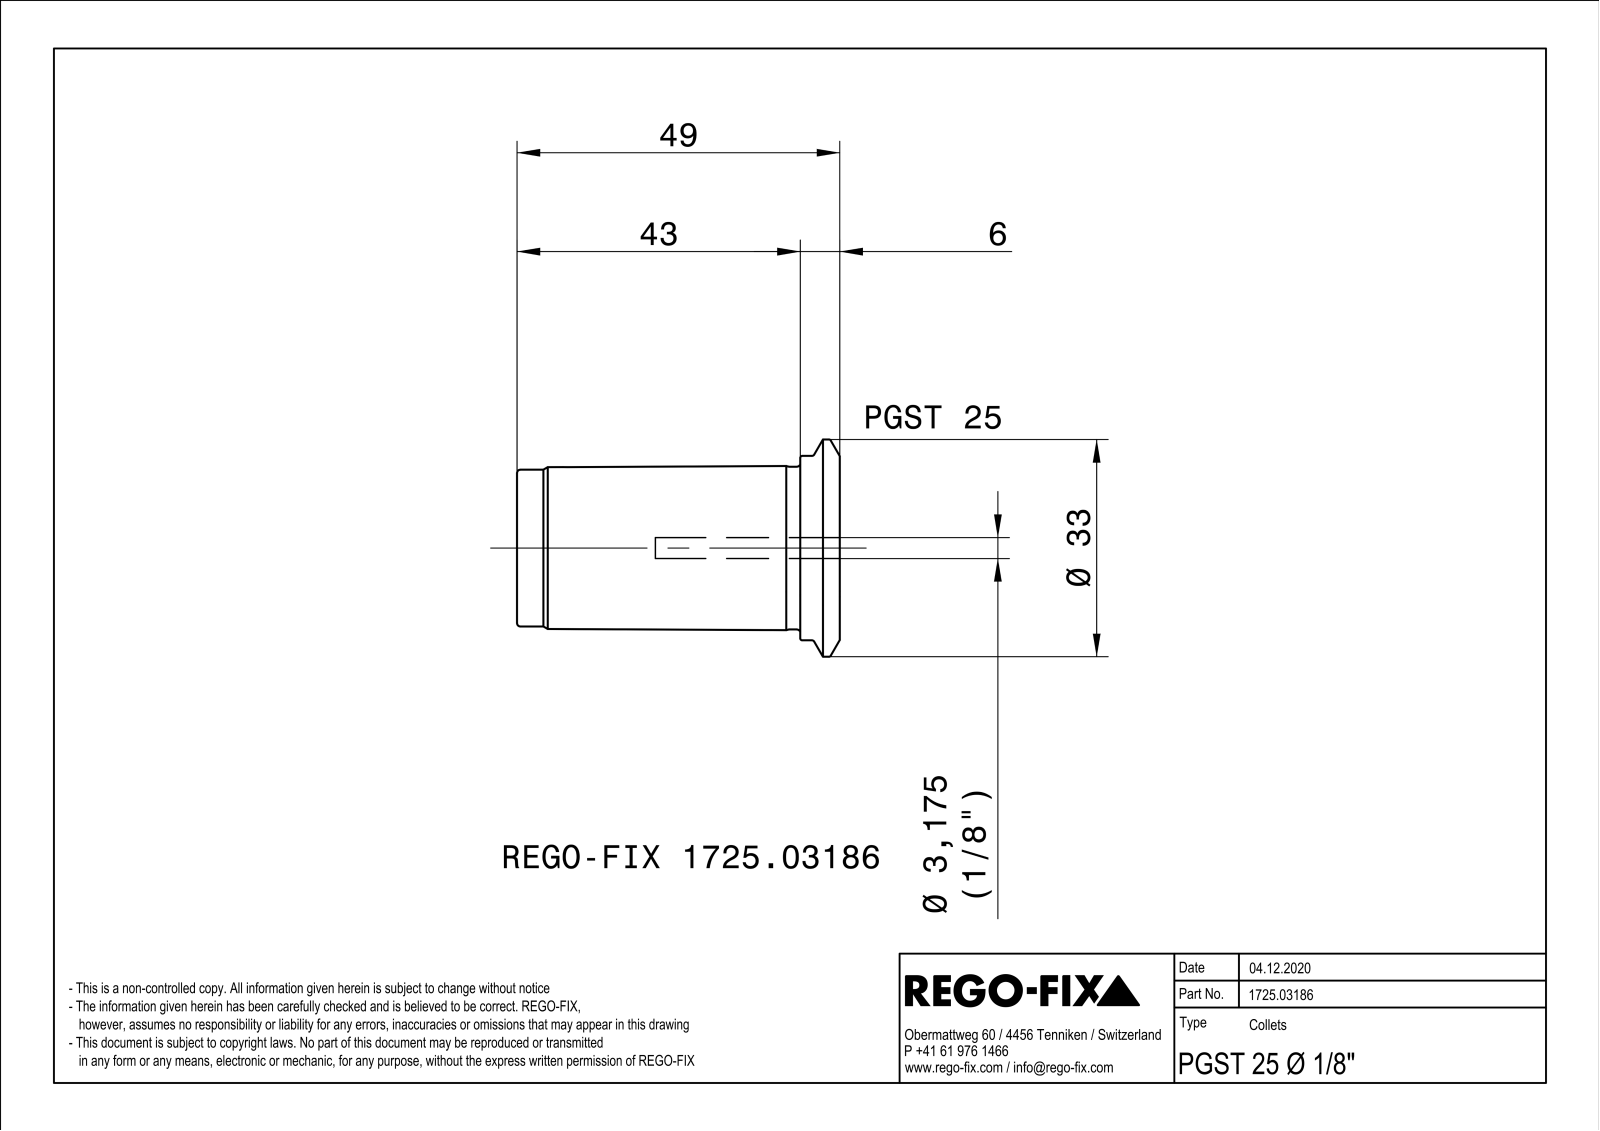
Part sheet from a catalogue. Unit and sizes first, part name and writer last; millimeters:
Units: millimetres
Overall size (bounding box): 49 × 32.98 × 32.98
Round holes (diameter × count): ⌀3 ×4, ⌀1.5 ×1, ⌀3.17 ×1, ⌀5.2 ×1, ⌀17 ×1, ⌀21.19 ×1, ⌀22.3 ×1
Round bosses / shafts (diameter × count): ⌀32.98 ×1, ⌀28 ×1, ⌀24.7 ×1, ⌀23.8 ×1, ⌀22 ×1, ⌀21 ×1, ⌀5 ×1, ⌀2.8 ×1
Main face-to-face distances: 43.5, 49, 5.5, 6, 37.5, 43, 28, 22, 15.5, 21
Hole centre spacings: 6.5, 11.26
Volume: 23 411 mm³ · Surface area: 7 877 mm²
Bodies: 2 solids, 56 faces (14 planar, 18 cylindrical, 24 other)
Part name (STEP PRODUCT): NOCUT
STEP written by: SIEMENS PLM Software Solid Edge ST10 (AUTOMOTIVE_DESIGN)
